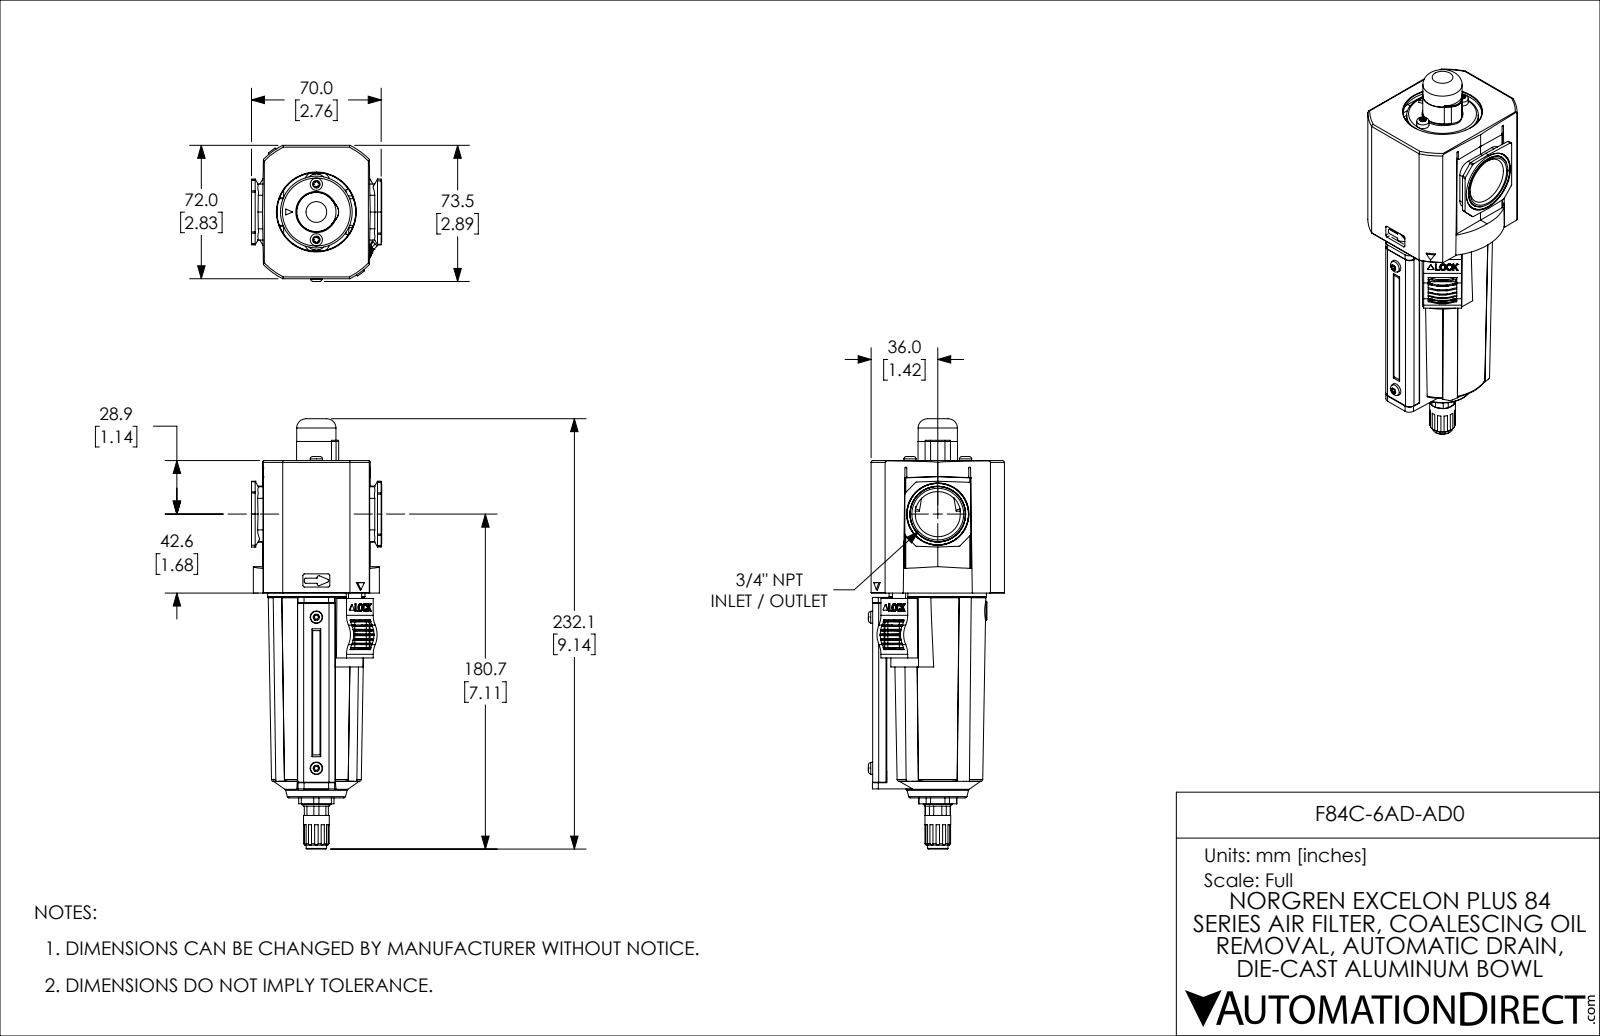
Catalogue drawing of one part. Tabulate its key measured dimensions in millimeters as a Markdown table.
| quantity | value |
| --- | --- |
| part name | F84C-6AD-AD0 |
| STEP written by | SolidWorks 2021 (CONFIG_CONTROL_DESIGN) |
| units | millimeters |
| bodies | 8 solids, 1363 faces (594 planar, 515 cylindrical, 254 other) |
| overall size | 232.1 × 73.5 × 70.3 |
| volume | 477 800 mm³ |
| surface area | 113 000 mm² |
| round holes (diameter × count) | 2.8 × 2, 4.1 × 2, 4.5 × 2, 5.6 × 1, 6.2 × 1, 16.1 × 1, 19.7 × 1, 62.5 × 1 |
| round bosses / shafts (diameter × count) | 8 × 2, 7 × 2, 6.6 × 2, 5.4 × 2, 53.9 × 1, 52.5 × 1, 51.3 × 1, 49.8 × 1 |
| partial cylindrical surfaces (radius × count) | 1 × 58, 0.5 × 57, 0.7 × 28, 0.3 × 18, 0.2 × 8, 1 × 8, 1.1 × 8, 1.5 × 8 |
| main face-to-face distances | 52, 9.6, 62.4, 72, 61.2, 49.6, 11.7, 1.5, 9.2, 40.3 |
| hole center spacings | 15, 15.1, 30.1, 30, 30.2, 63.6 |
